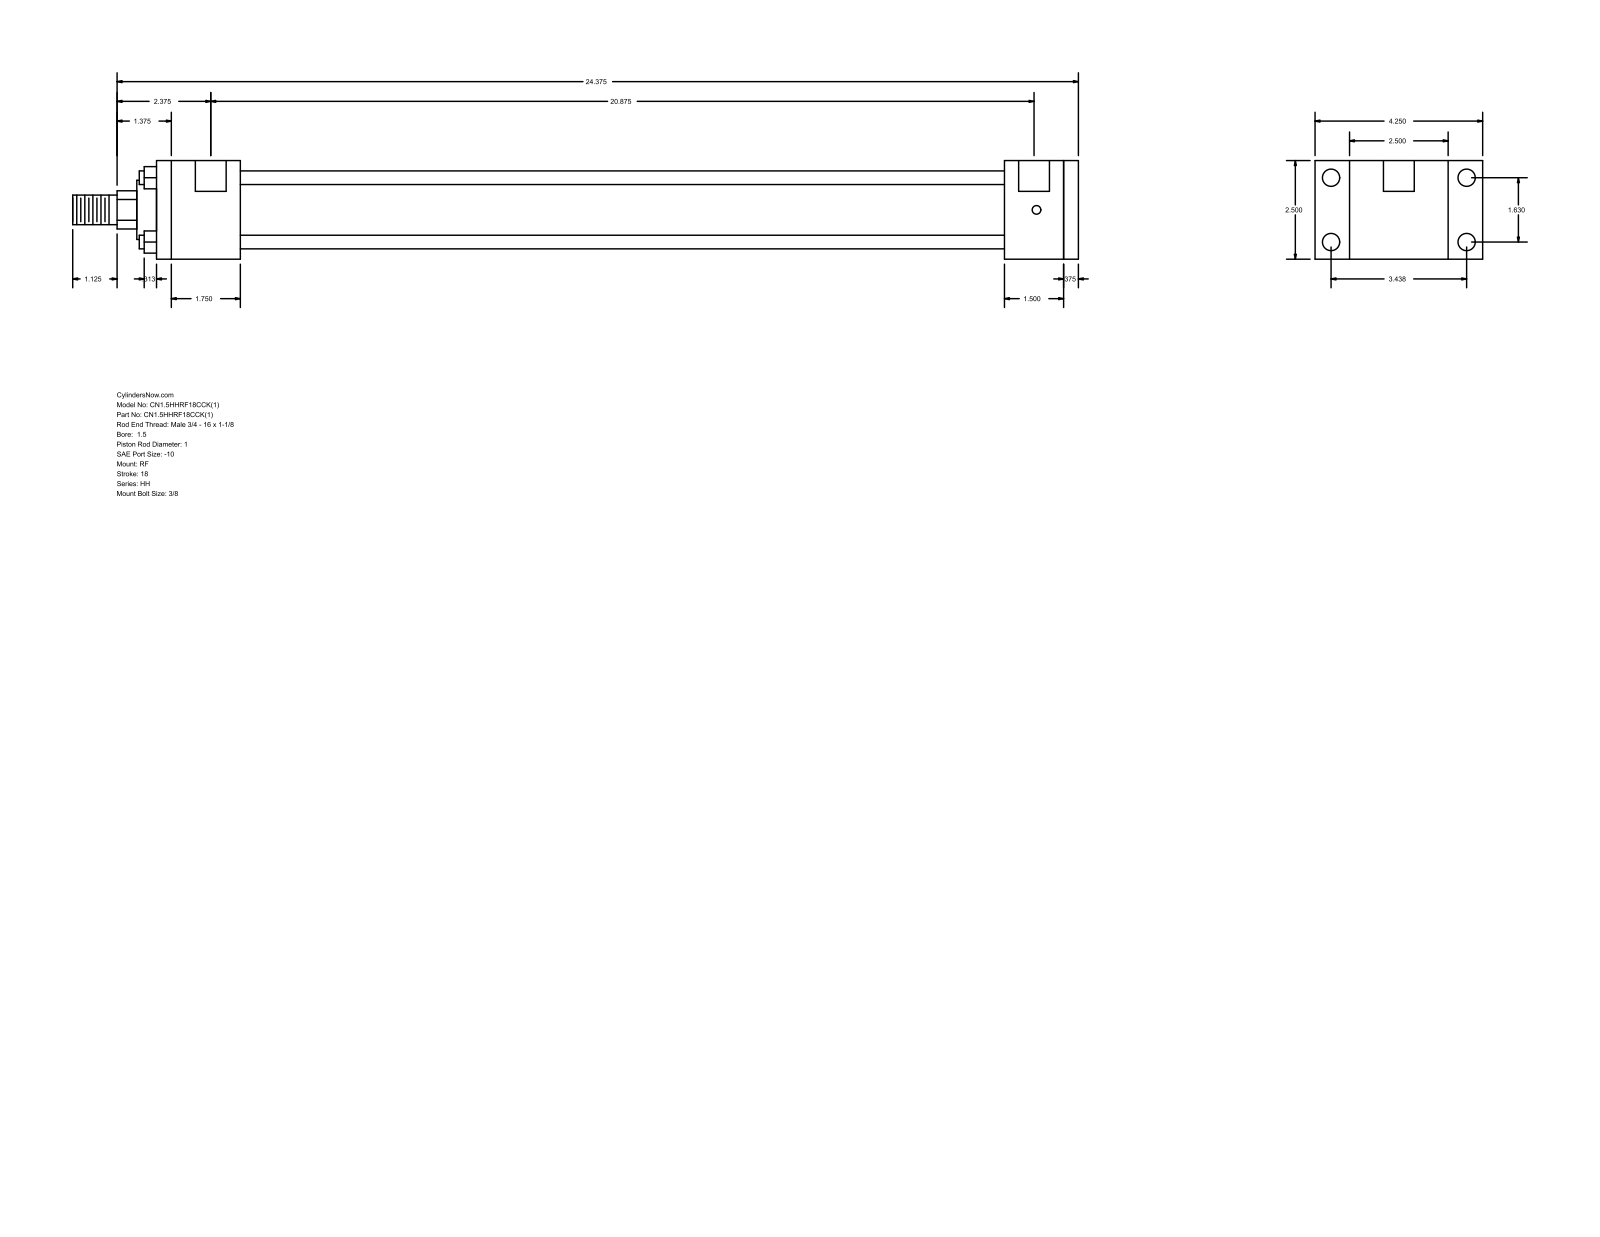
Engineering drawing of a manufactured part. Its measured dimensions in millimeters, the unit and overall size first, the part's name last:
Units: millimetres
Overall size (bounding box): 647.7 × 107.95 × 63.5
Round holes (diameter × count): ⌀5.56 ×4, ⌀11.13 ×4, ⌀19.84 ×2
Round bosses / shafts (diameter × count): ⌀8.76 ×4, ⌀44.45 ×1, ⌀38.1 ×1, ⌀25.4 ×1, ⌀19.05 ×1
Partial cylindrical surfaces — rounded edges, fillets, slot ends (radius × count): R12.29 ×1
Main face-to-face distances: 63.5, 9.52, 38.1, 492.12, 530.22, 539.74, 47.62, 53.98, 546.1, 584.2
Hole centre spacings: 1.59, 41.4, 87.32, 96.64, 531.81, 533.4, 530.22
Bodies: 0 solids, 92 faces (64 planar, 28 cylindrical, 0 other)
Part name (STEP PRODUCT): HH_RF__0150_1
STEP written by: GSSL Pune (CONFIG_CONTROL_DESIGN)
